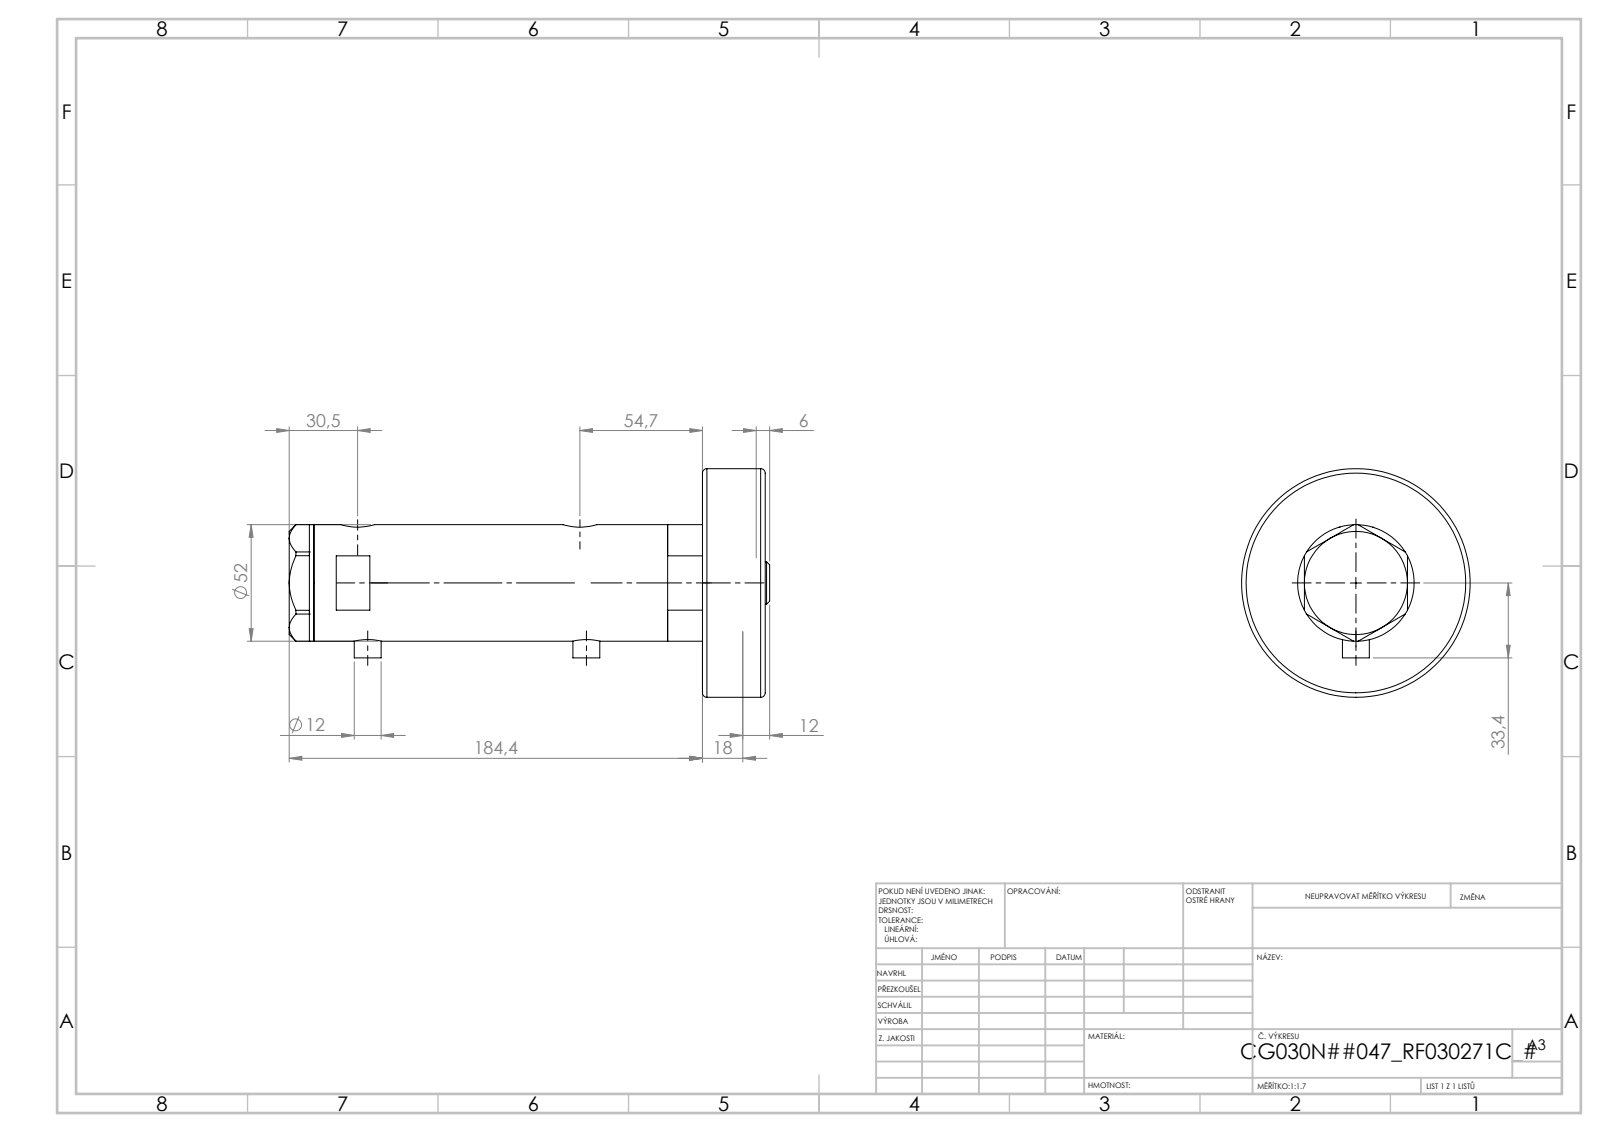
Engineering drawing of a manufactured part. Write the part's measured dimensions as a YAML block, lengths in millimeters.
part_name: "V270CG_BACK; V270CG_MIDDLE; V270CG_FRONT; V270CG_VC"
step_written_by: "SolidWorks 2019 (CONFIG_CONTROL_DESIGN)"
units: millimeters
bodies: {solids: 4, faces: 140, planar: 67, cylindrical: 53, other: 20}
overall_size: [196.02, 53.1, 52]
volume: 348877
surface_area: 80150
round_holes:
  - {diameter: 5, count: 2}
  - {diameter: 9.73, count: 2}
  - {diameter: 12.5, count: 2}
  - {diameter: 15, count: 2}
  - {diameter: 6.5, count: 1}
  - {diameter: 20, count: 1}
  - {diameter: 21.5, count: 1}
  - {diameter: 30, count: 1}
  - {diameter: 33, count: 1}
  - {diameter: 44, count: 1}
round_bosses_or_shafts:
  - {diameter: 12, count: 2}
  - {diameter: 52, count: 1}
  - {diameter: 40, count: 1}
  - {diameter: 38, count: 1}
  - {diameter: 19, count: 1}
face_to_face_distances: [100.54, 23.8, 76.74, 11, 34.8, 111.54, 46, 147.94, 136.94, 113.14]
hole_center_spacings: [2.9, 4.5, 73.75, 76.65, 78.25, 81.15, 2.89, 2.91]
